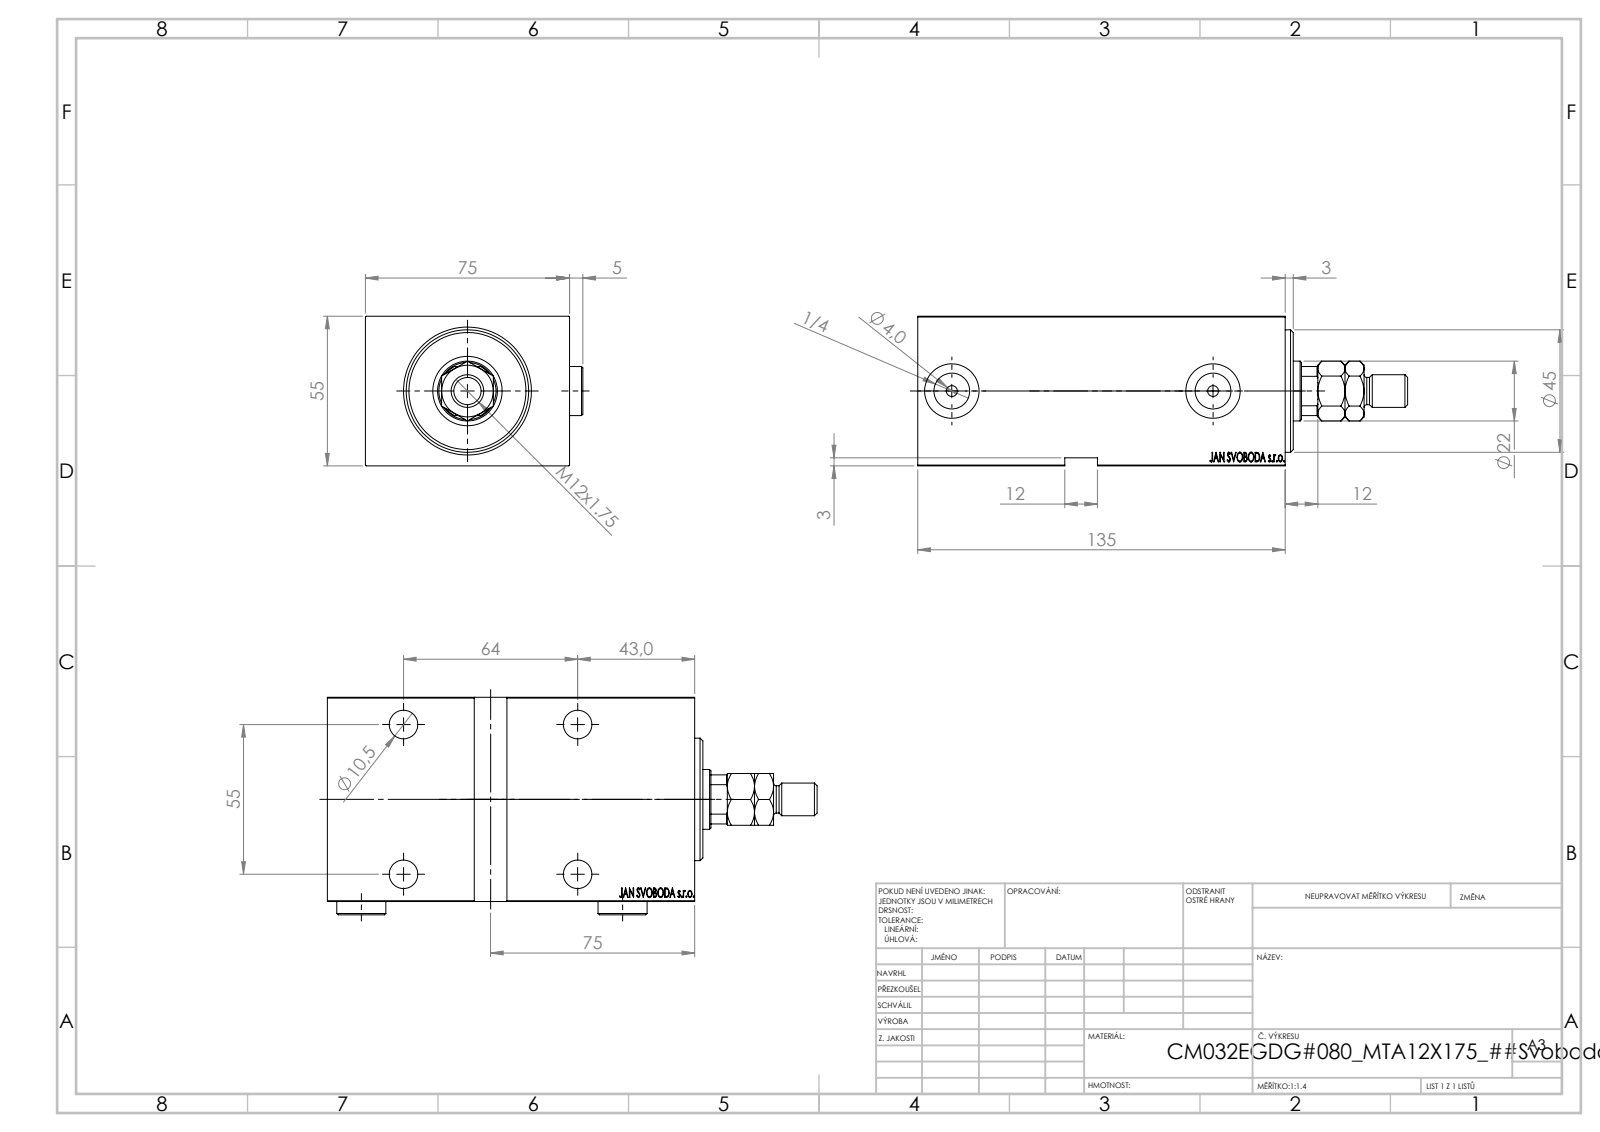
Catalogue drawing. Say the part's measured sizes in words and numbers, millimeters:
The part is named "V450CM_VC_B; MTA; V450CM_E_Body; V450CM_E_VCP (+1 more)". Its 3-D file was written by "SolidWorks 2019 (CONFIG_CONTROL_DESIGN)". It is 6 solids with 958 faces: 460 planar, 70 cylindrical and 428 other. Overall it measures 180 by 79.9 by 55 millimeters. Its volume is 503 674 cubic millimeters and its surface area 89 463 square millimeters. Round holes: 5 of diameter 10.5, 4 of diameter 16.5, 2 of diameter 4, 2 of diameter 13.16, 2 of diameter 20, 1 of diameter 22, 1 of diameter 25.5, 1 of diameter 32, 1 of diameter 45. Round bosses or shafts: 2 of diameter 18, 1 of diameter 34, 1 of diameter 12, 1 of diameter 10. Partial cylindrical surfaces (rounded edges, fillets, slot ends): 1 of radius 10.5. The main face-to-face distances are 55, 75, 135, 3, 5, 10, 125, 130, 120, 74.9. The hole center spacings are 55, 64, 84.39, 96.
